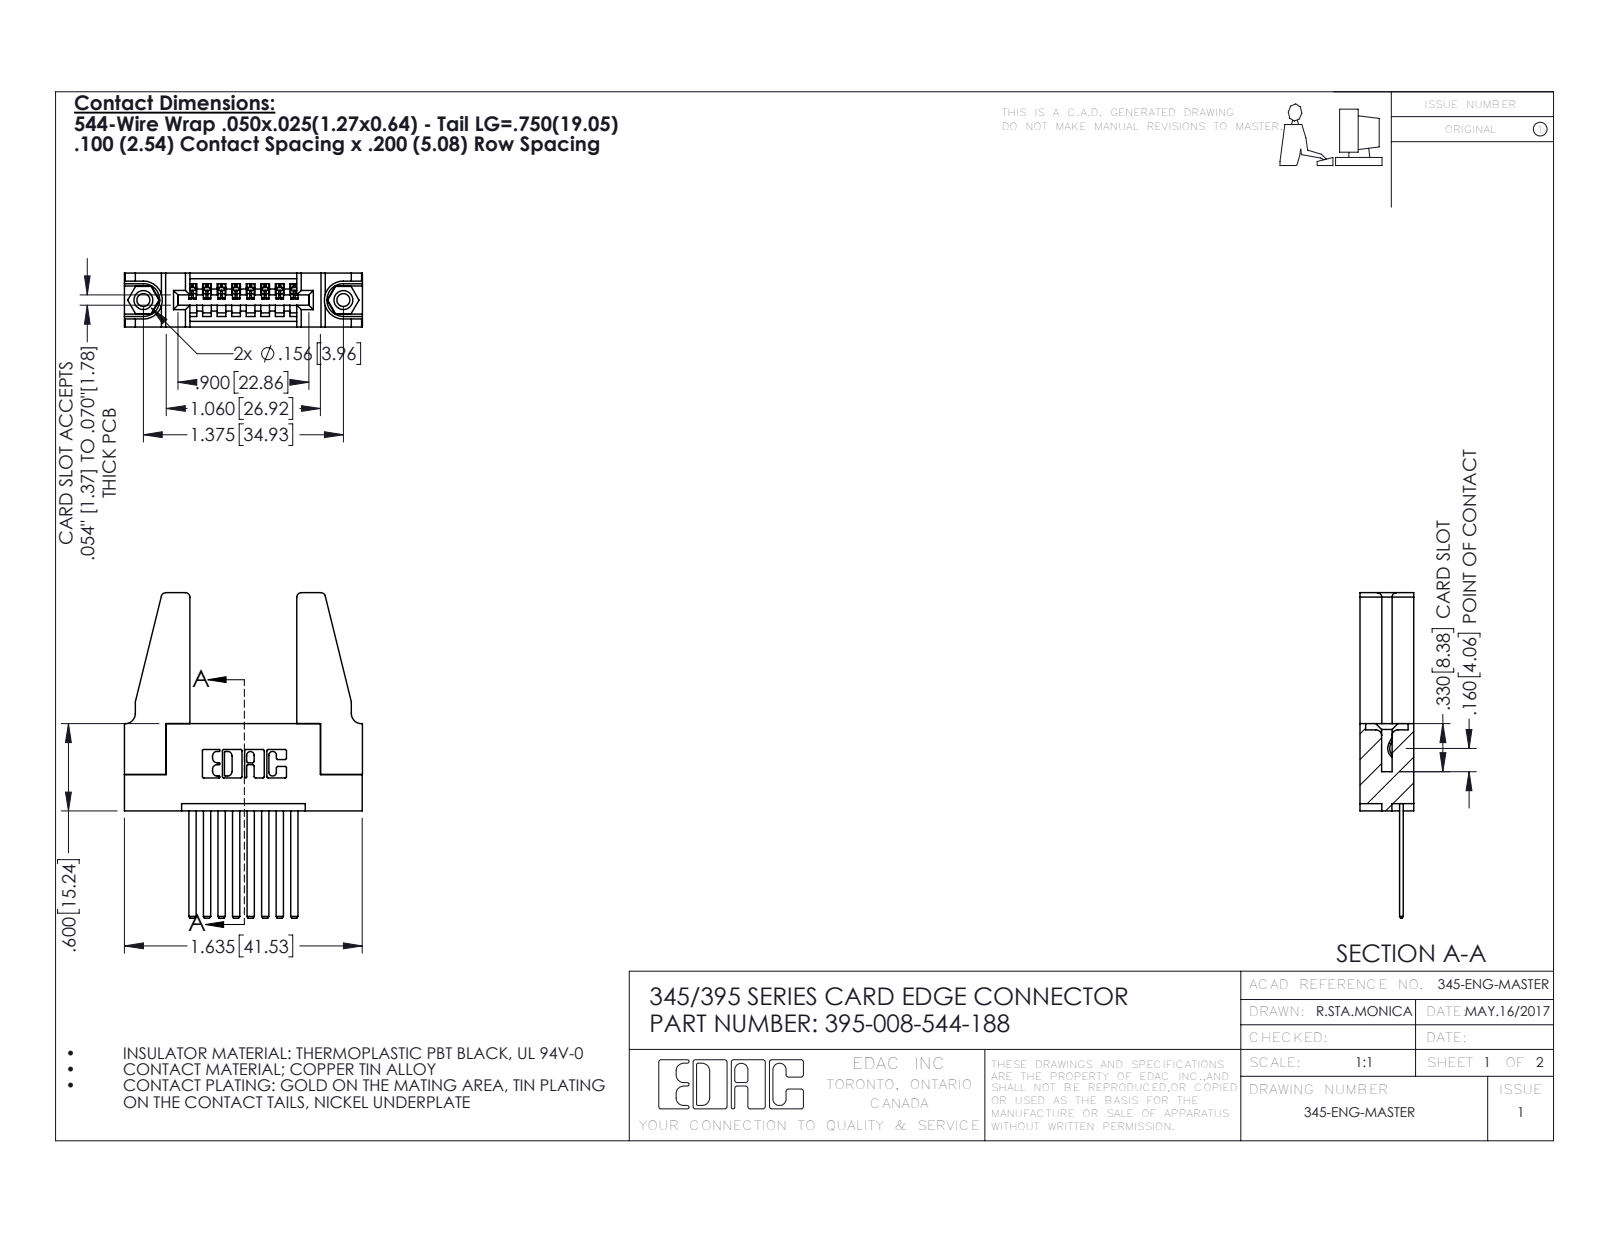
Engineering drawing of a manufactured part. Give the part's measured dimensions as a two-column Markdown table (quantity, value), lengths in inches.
| quantity | value |
| --- | --- |
| part name | 345-220-078_345-220-088; 345-292-001_345-293-144; 345-250-001_345-250-001-102; 395-008-544-188 (+1 more) |
| STEP written by | SolidWorks 2016 (CONFIG_CONTROL_DESIGN) |
| units | inches |
| bodies | 13 solids, 666 faces (440 planar, 210 cylindrical, 16 other) |
| overall size | 2.237 × 1.636 × 0.37 |
| volume | 0.428 in³ |
| surface area | 12.31 in² |
| round holes (diameter × count) | 0.089 × 2, 0.125 × 2, 0.156 × 2, 0.064 × 1 |
| round bosses / shafts (diameter × count) | 0.155 × 2 |
| partial cylindrical surfaces (radius × count) | 0.01 × 22, 0.006 × 16, 0.03 × 8, 0.007 × 6, 0.031 × 6, 0.026 × 3, 0.031 × 2, 0.04 × 2 |
| main face-to-face distances | 0.37, 0.072, 0.298, 0.2, 0.098, 0.272, 0.025, 0.15, 0.148, 0.35 |
| hole center spacings | 0.27, 1.144, 1.375 |
